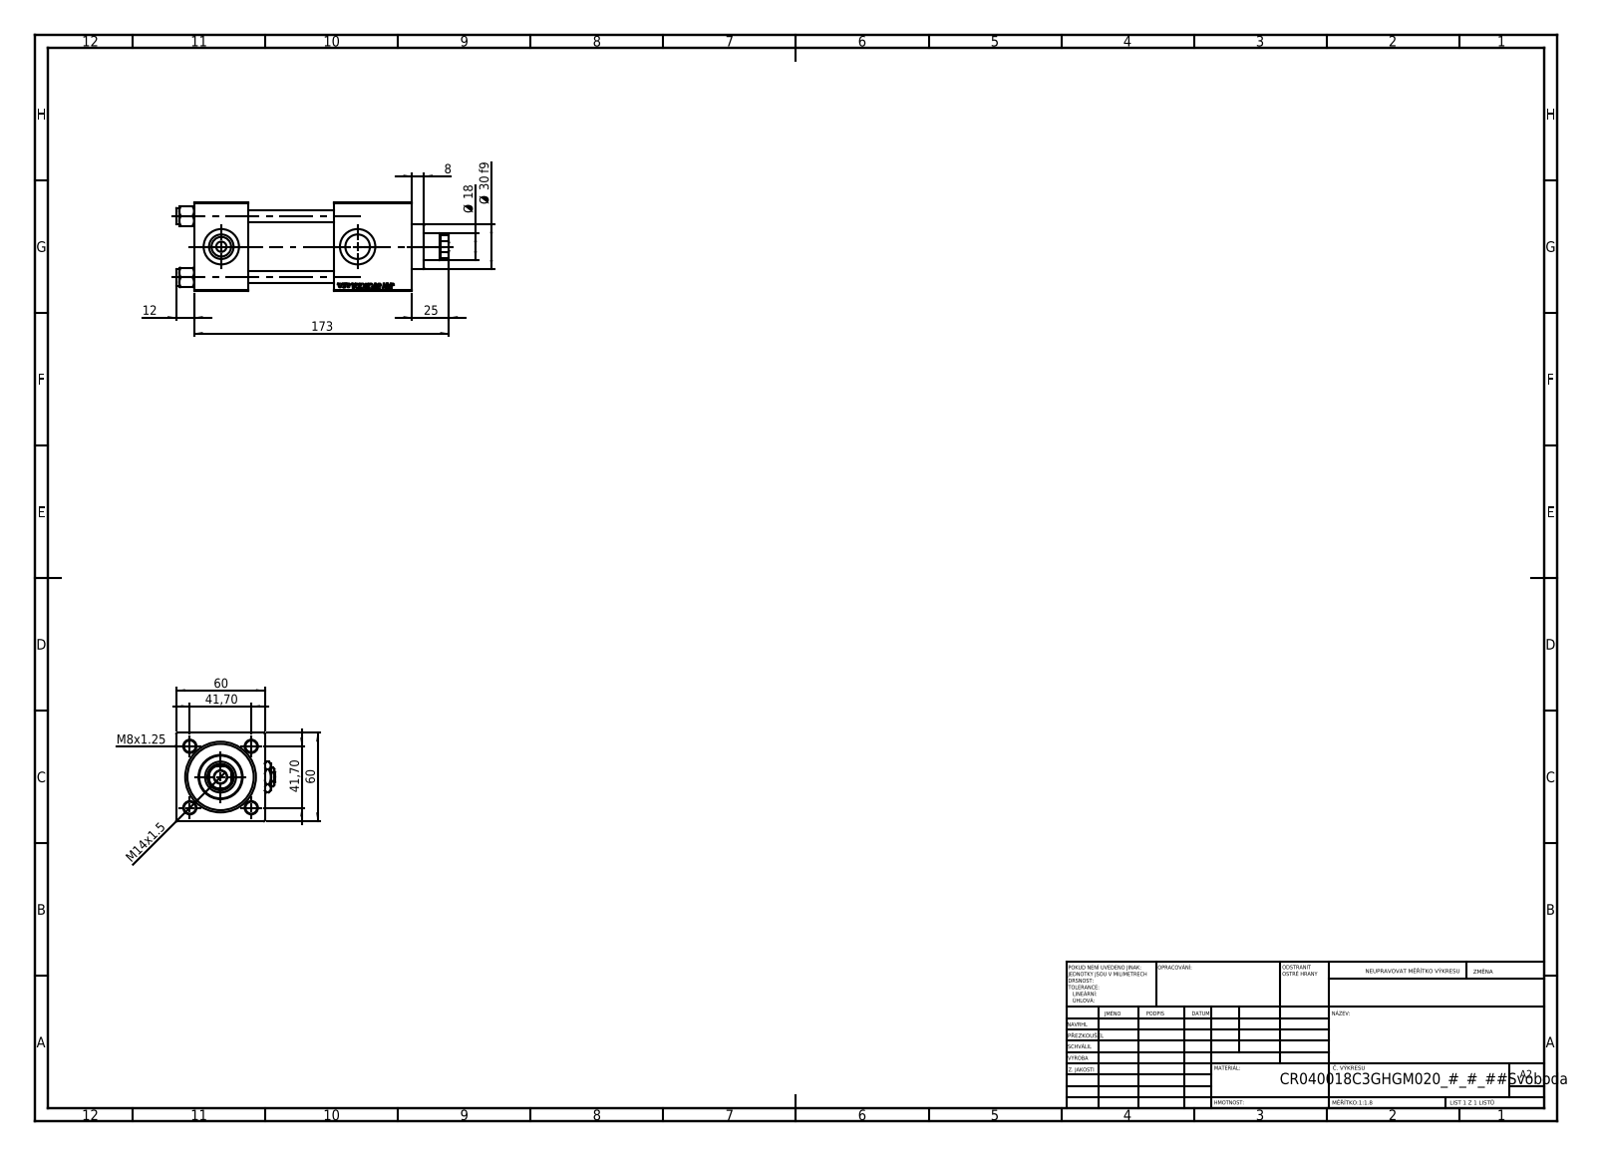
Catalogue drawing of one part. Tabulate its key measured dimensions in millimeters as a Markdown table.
| quantity | value |
| --- | --- |
| part name | V215CR_VCP_C; V215CR_C_Body; V215_VC_A; NUT_M5_C (+2 more) |
| STEP written by | SolidWorks 2019 (CONFIG_CONTROL_DESIGN) |
| units | millimeters |
| bodies | 13 solids, 1250 faces (574 planar, 98 cylindrical, 578 other) |
| overall size | 185 × 67 × 60 |
| volume | 399 322 mm³ |
| surface area | 108 248 mm² |
| round holes (diameter × count) | 8 × 4, 7 × 2, 16.66 × 2, 24 × 2, 8.5 × 1, 18 × 1, 21 × 1, 31 × 1, 40 × 1, 45 × 1 |
| round bosses / shafts (diameter × count) | 11 × 4, 46 × 1, 30 × 1 |
| partial cylindrical surfaces (radius × count) | 8.5 × 1 |
| main face-to-face distances | 60, 37, 53, 148, 111, 58, 95, 119.3, 82.3, 24.3 |
| hole center spacings | 29.49, 41.7, 58.97, 92.5 |
